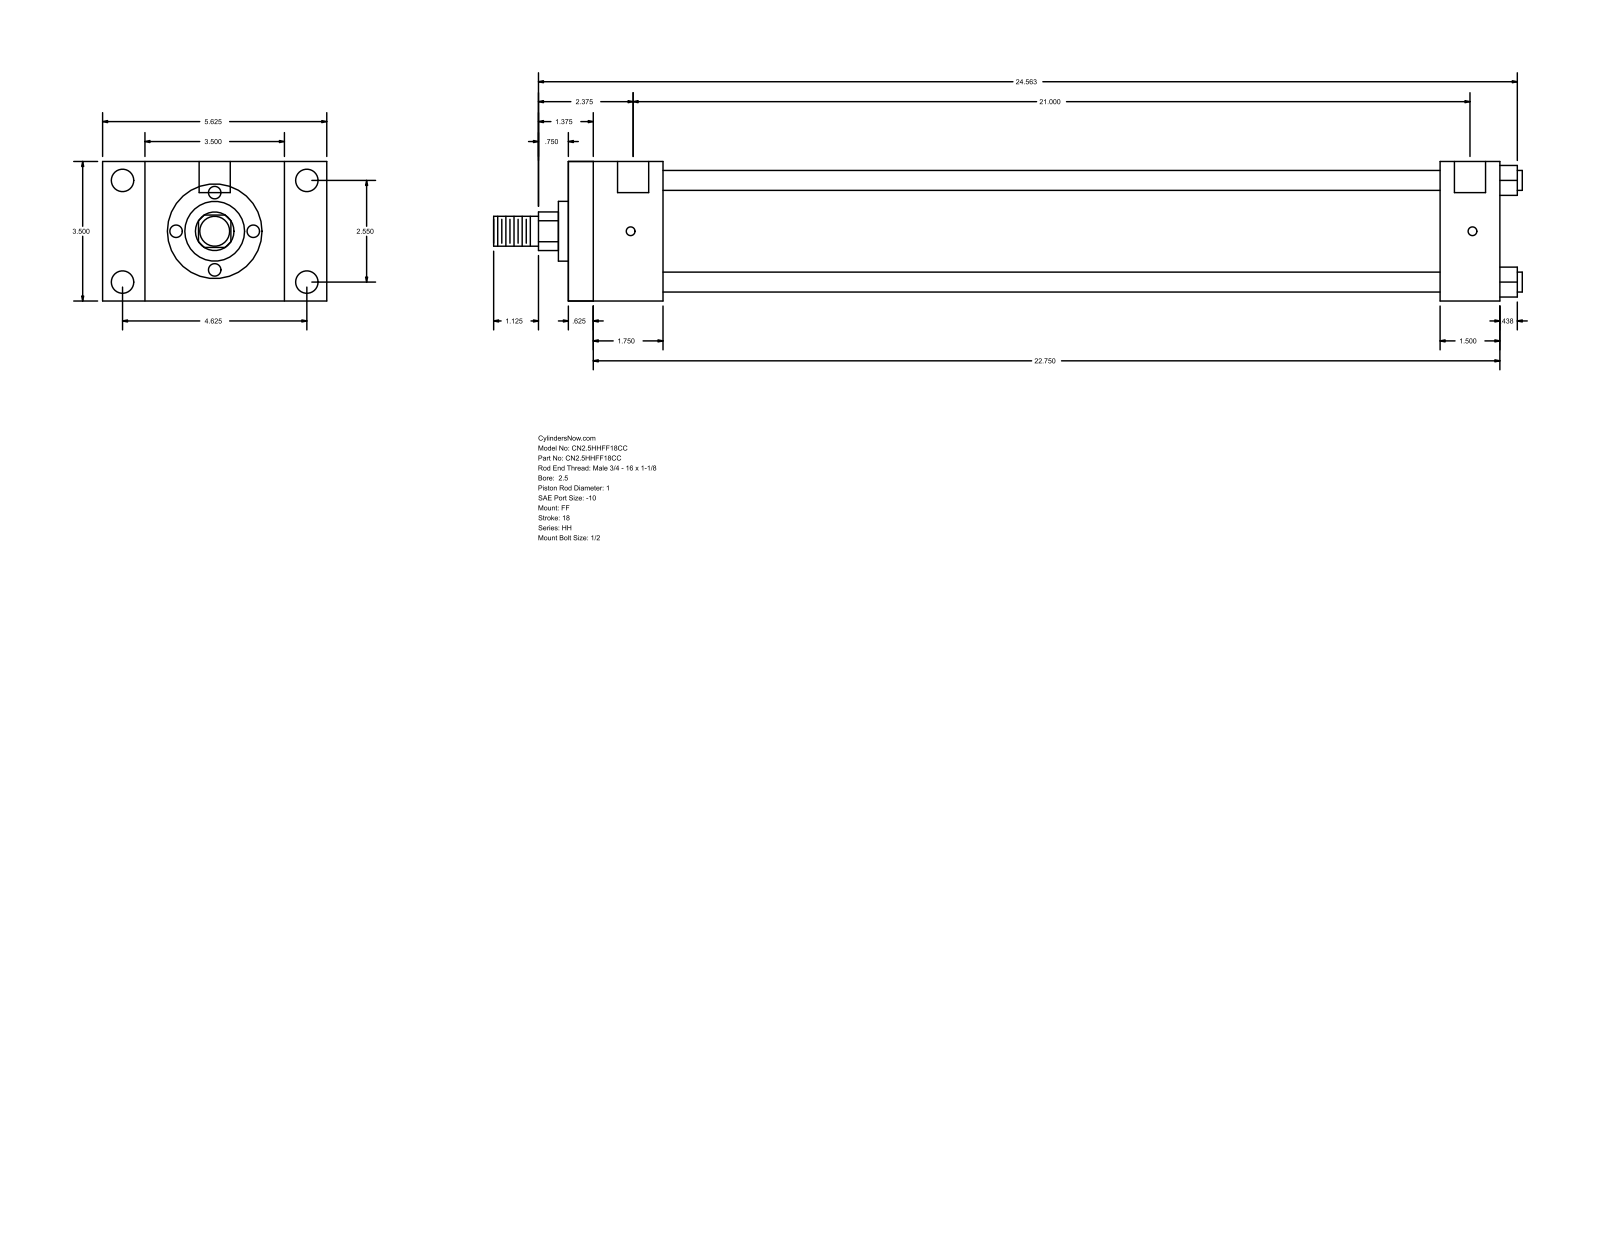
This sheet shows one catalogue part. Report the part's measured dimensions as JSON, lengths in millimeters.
{"part_name": "HH_FF__0250_1", "step_written_by": "GSSL Pune (CONFIG_CONTROL_DESIGN)", "units": "millimeters", "bodies": {"solids": 0, "faces": 92, "planar": 64, "cylindrical": 28, "other": 0}, "overall_size": [655.64, 142.88, 88.9], "round_holes": [[5.56, 4], [14.3, 4], [19.84, 2]], "round_bosses_or_shafts": [[12.7, 4], [73.03, 1], [38.1, 1], [25.4, 1], [19.05, 1]], "partial_cylinders_radius": [[12.29, 1]], "face_to_face_distances": [88.9, 593.72, 15.87, 577.85, 38.1, 60.33, 44.46, 533.39, 555.62, 539.75], "hole_center_spacings": [64.76, 117.48, 134.15, 536.57, 1.58, 1.59, 533.4, 534.98]}
